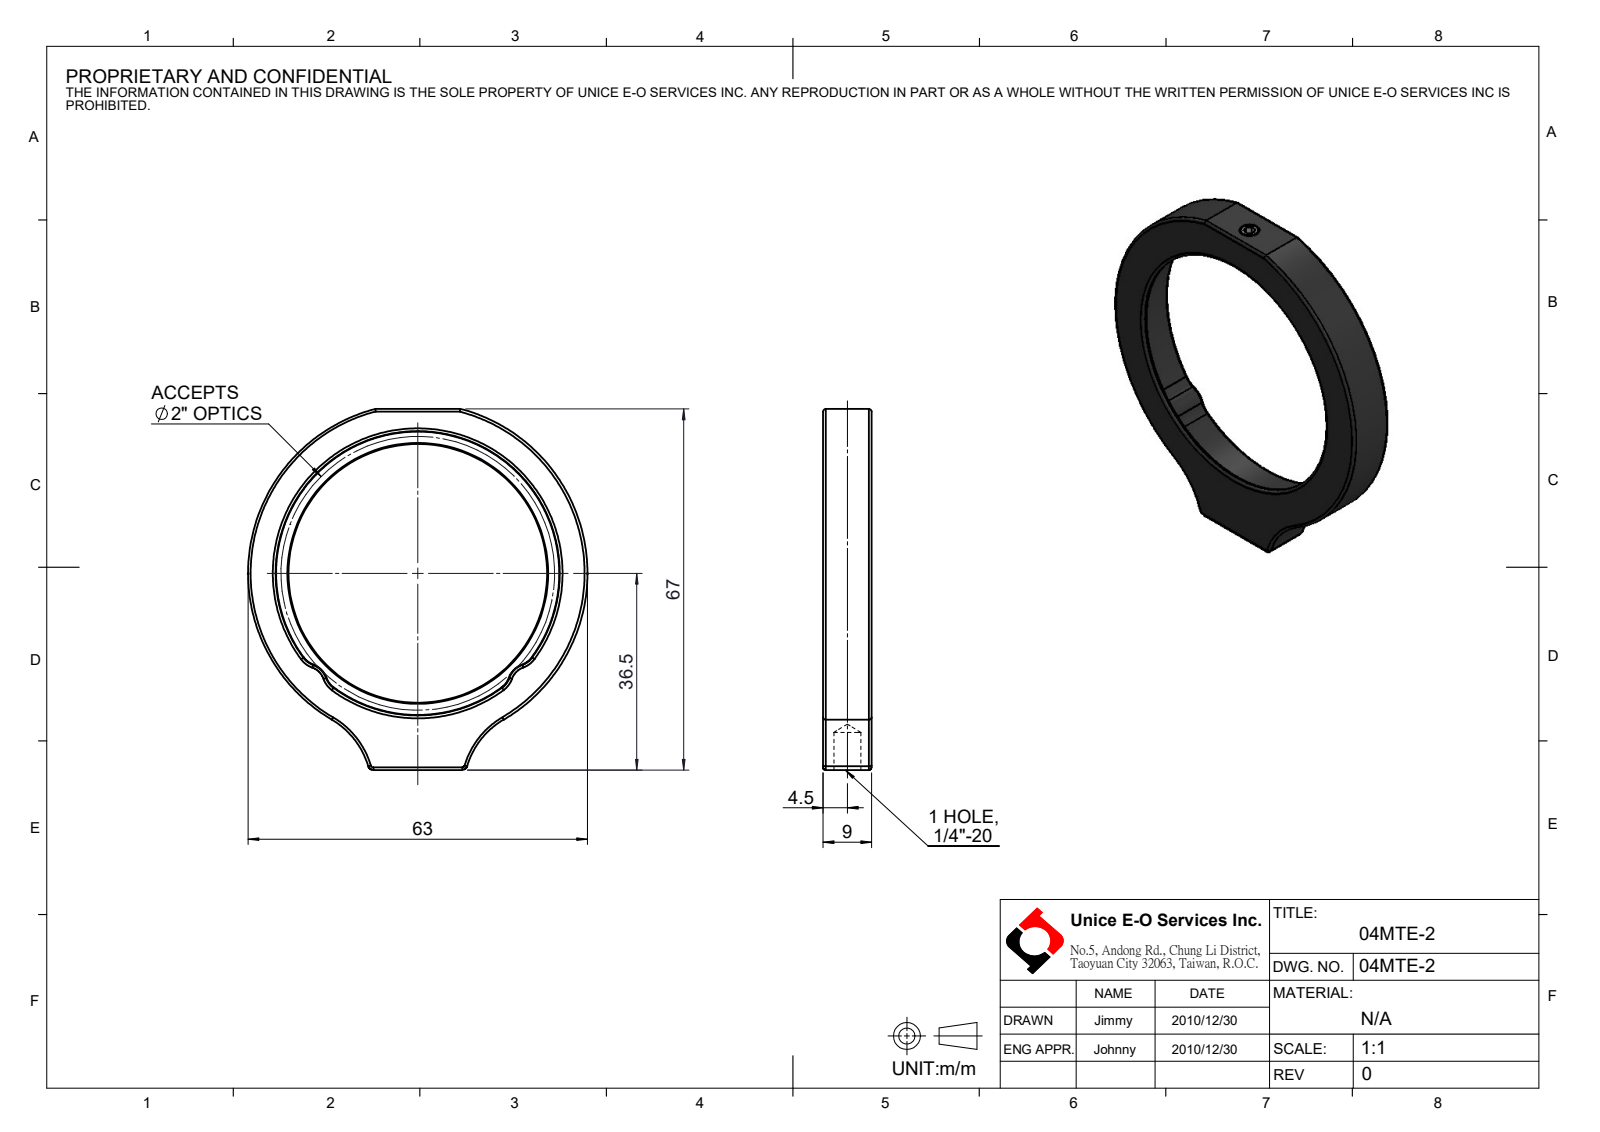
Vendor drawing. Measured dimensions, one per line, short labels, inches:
name: 04MTE-2
written by: SolidWorks 2016 (CONFIG_CONTROL_DESIGN)
unit: in
bodies: 3 solids, 95 faces (16 planar, 33 cylindrical, 46 other)
size: 2.638 × 2.48 × 0.354
volume: 0.585 in³; area: 9.686 in²
holes: 1× ⌀0.059, 1× ⌀0.13, 1× ⌀0.201, 1× ⌀1.89, 1× ⌀2.079
bosses: 1× ⌀0.157, 1× ⌀0.063
rounds: 6× R0.157, 4× R0.02, 2× R0.039, 2× R0.591, 1× R1.24
face distances: 0.354, 0.039, 0.315, 2.638, 0.079, 2.48, 0.157, 0.098, 2.539, 0.059
hole spacings: 0.02
